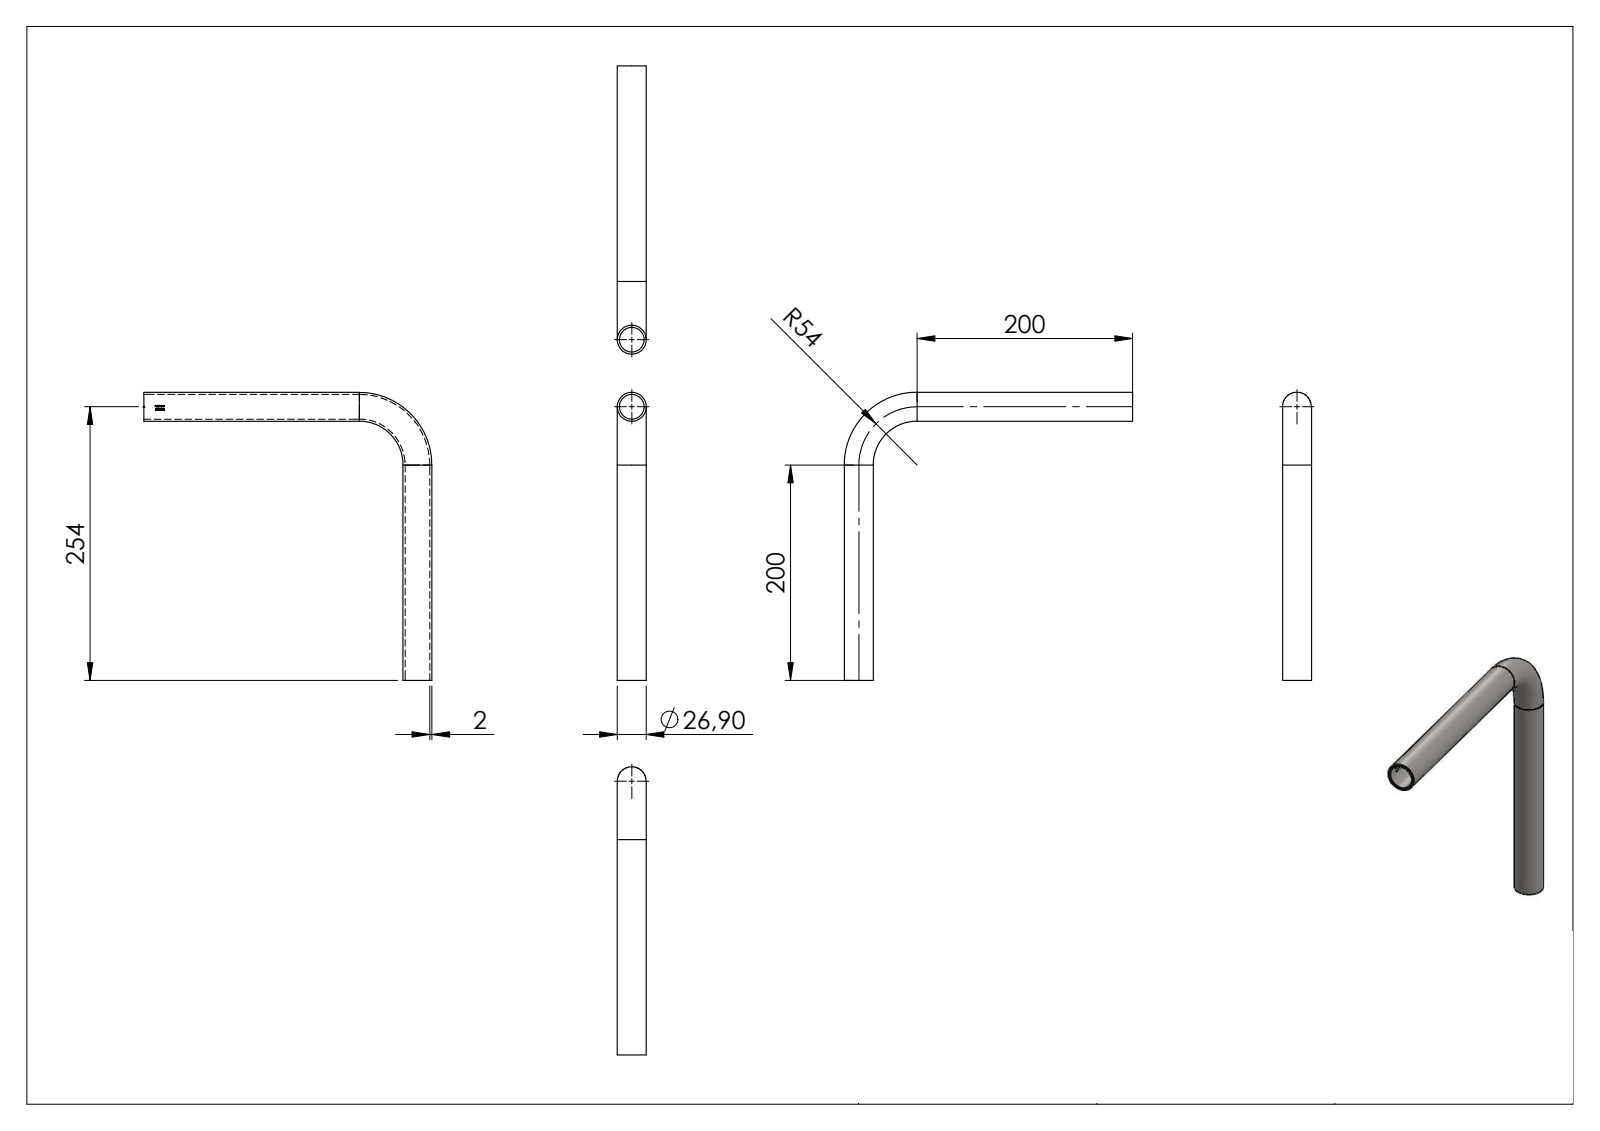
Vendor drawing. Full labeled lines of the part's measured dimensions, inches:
Part name (STEP PRODUCT): 55110-090
STEP written by: SolidWorks 2015 (CONFIG_CONTROL_DESIGN)
Units: inches
Bodies: 1 solid, 229 faces (87 planar, 38 cylindrical, 104 other)
Overall size (bounding box): 10.53 × 10.53 × 1.059
Volume: 4.629 in³ · Surface area: 118.1 in²
Round holes (diameter × count): ⌀0.902 ×2
Round bosses / shafts (diameter × count): ⌀1.059 ×2
Partial cylindrical surfaces — rounded edges, fillets, slot ends (radius × count): R0.455 ×1
Main face-to-face distances: 0.015, 0.05, 0.117, 0.167, 0.08, 0.055, 0.129, 0.094, 0.034, 0.126
